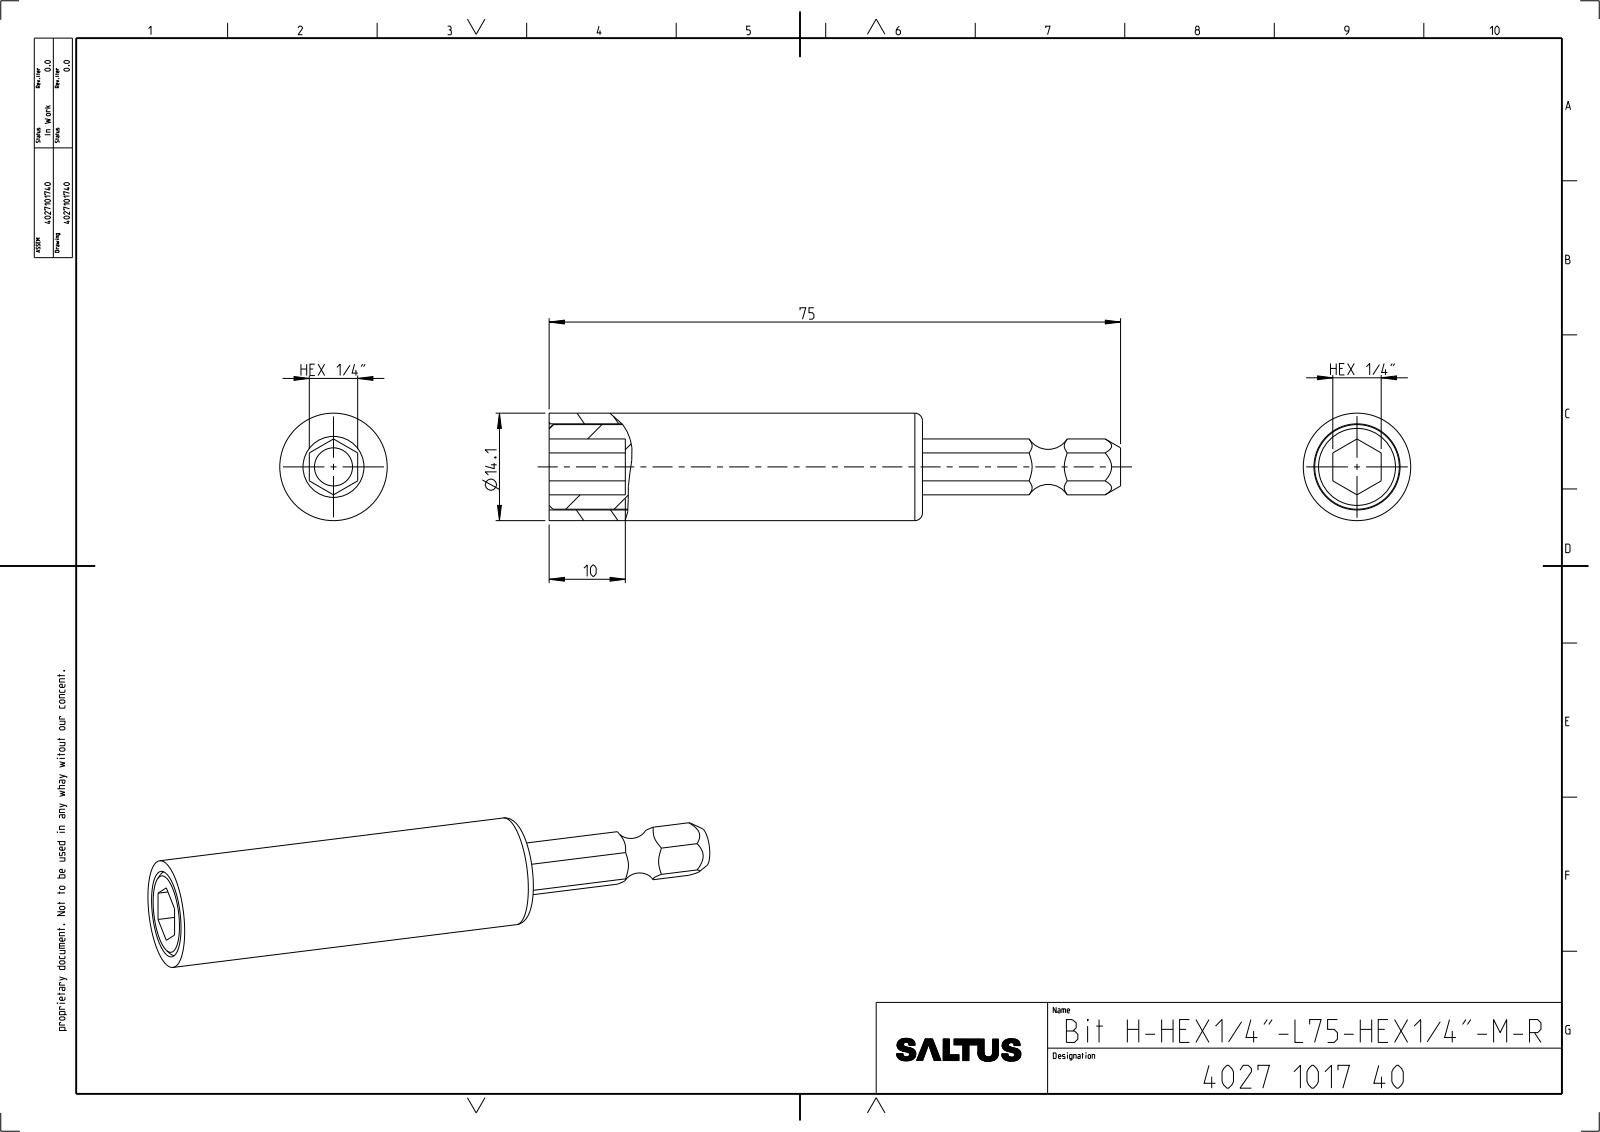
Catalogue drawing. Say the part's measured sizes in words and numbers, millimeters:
The part is named "4027911211; 4027299489; 4027101740_ASM". Its 3-D file was written by "CREO PARAMETRIC BY PTC INC, 2022414 (CONFIG_CONTROL_DESIGN)". It is 2 solids with 61 faces: 25 planar, 16 cylindrical and 20 other. Overall it measures 75 by 14.1 by 14.1 millimeters. Its volume is 7 753 cubic millimeters and its surface area 6 656 square millimeters. Round holes: 1 of diameter 8, 1 of diameter 11.3. Round bosses or shafts: 1 of diameter 14.1, 1 of diameter 11.1, 1 of diameter 10.5. The main face-to-face distances are 6.34, 49, 2.5, 46.5, 39, 36.5, 10, 26, 28.5, 65.
